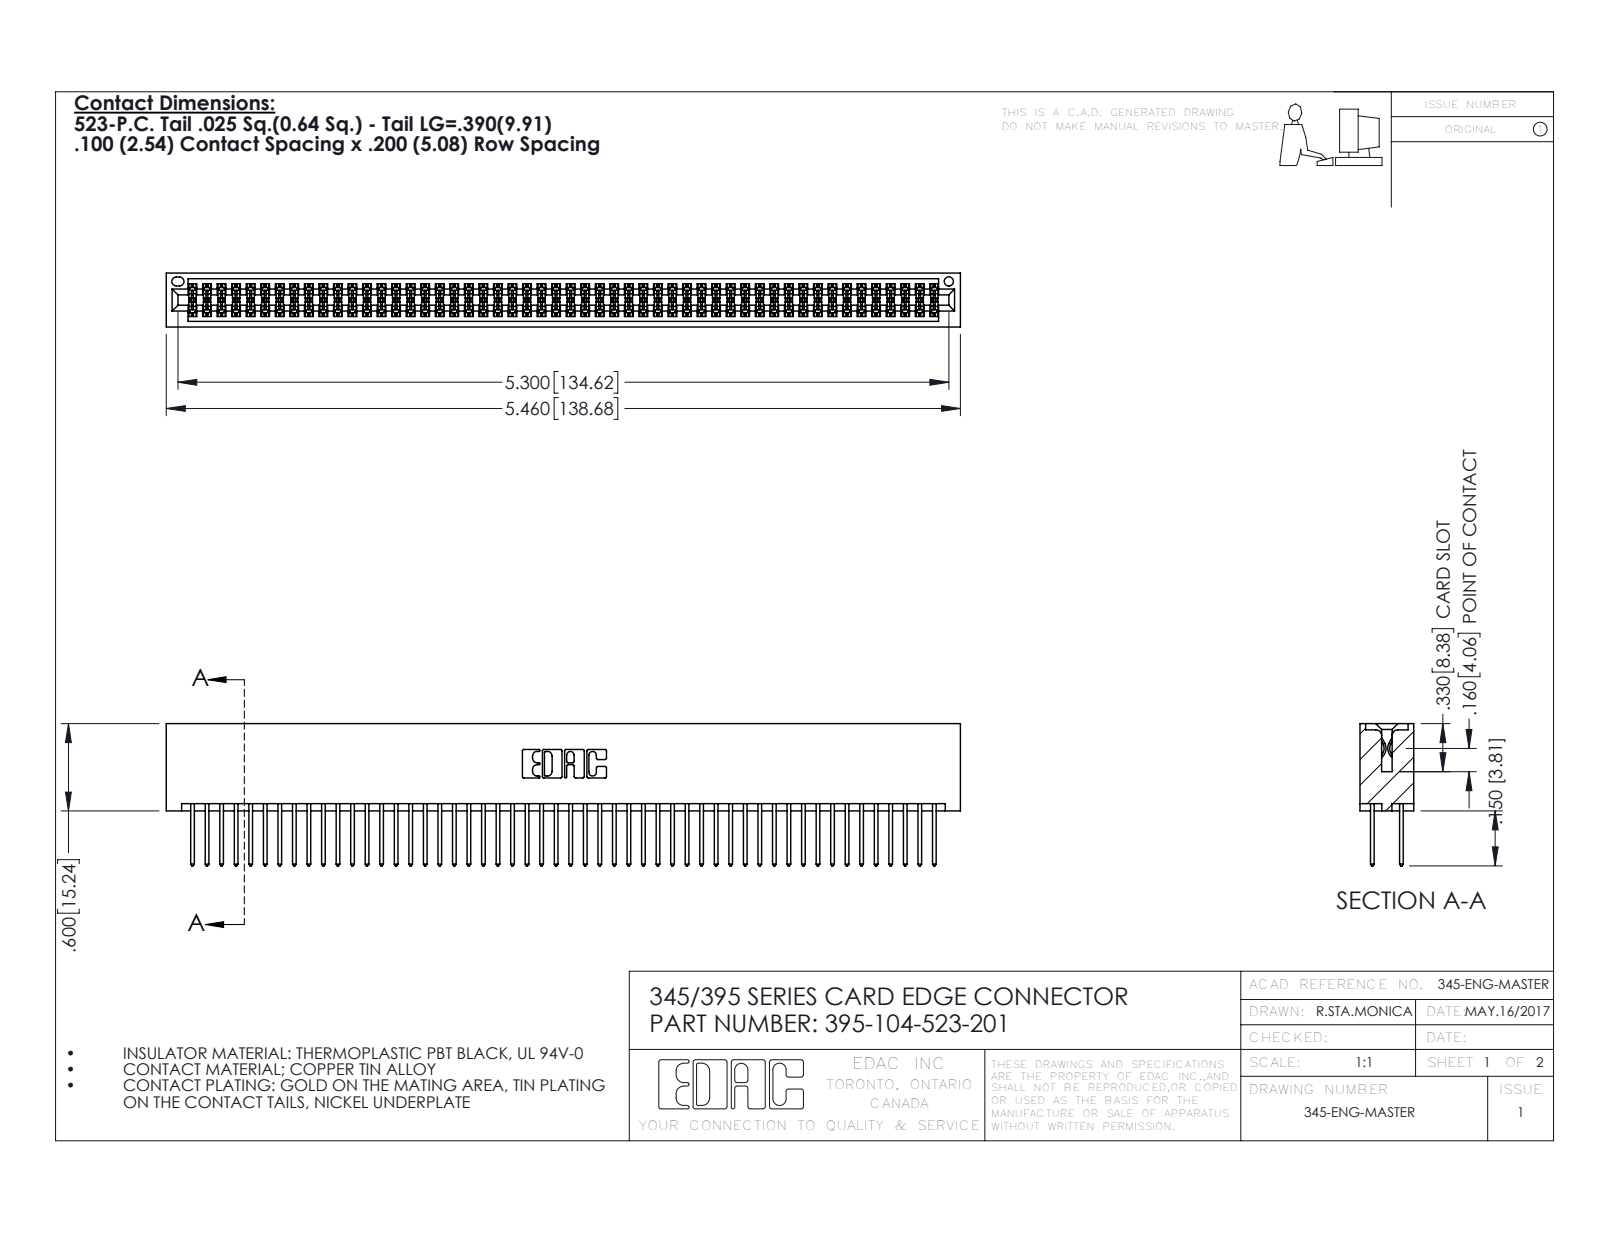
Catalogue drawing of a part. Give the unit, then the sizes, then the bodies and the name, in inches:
Units: inches
Overall size (bounding box): 5.46 × 0.977 × 0.37
Round holes (diameter × count): ⌀0.064 ×1
Partial cylindrical surfaces — rounded edges, fillets, slot ends (radius × count): R0.006 ×156, R0.01 ×104, R0.01 ×22, R0.007 ×6, R0.031 ×6, R0.026 ×3, R0.014 ×2, R0.019 ×2
Main face-to-face distances: 0.298, 0.072, 0.2, 0.098, 0.272, 0.025, 0.37, 0.225, 0.175, 0.149
Volume: 0.878 in³ · Surface area: 35.23 in²
Bodies: 105 solids, 5318 faces (3508 planar, 1810 cylindrical, 0 other)
Part name (STEP PRODUCT): 395-104-523-201; 345 Part_No Mounting Lugs; 345-292-001_345-293-123
STEP written by: SolidWorks 2016 (CONFIG_CONTROL_DESIGN)
